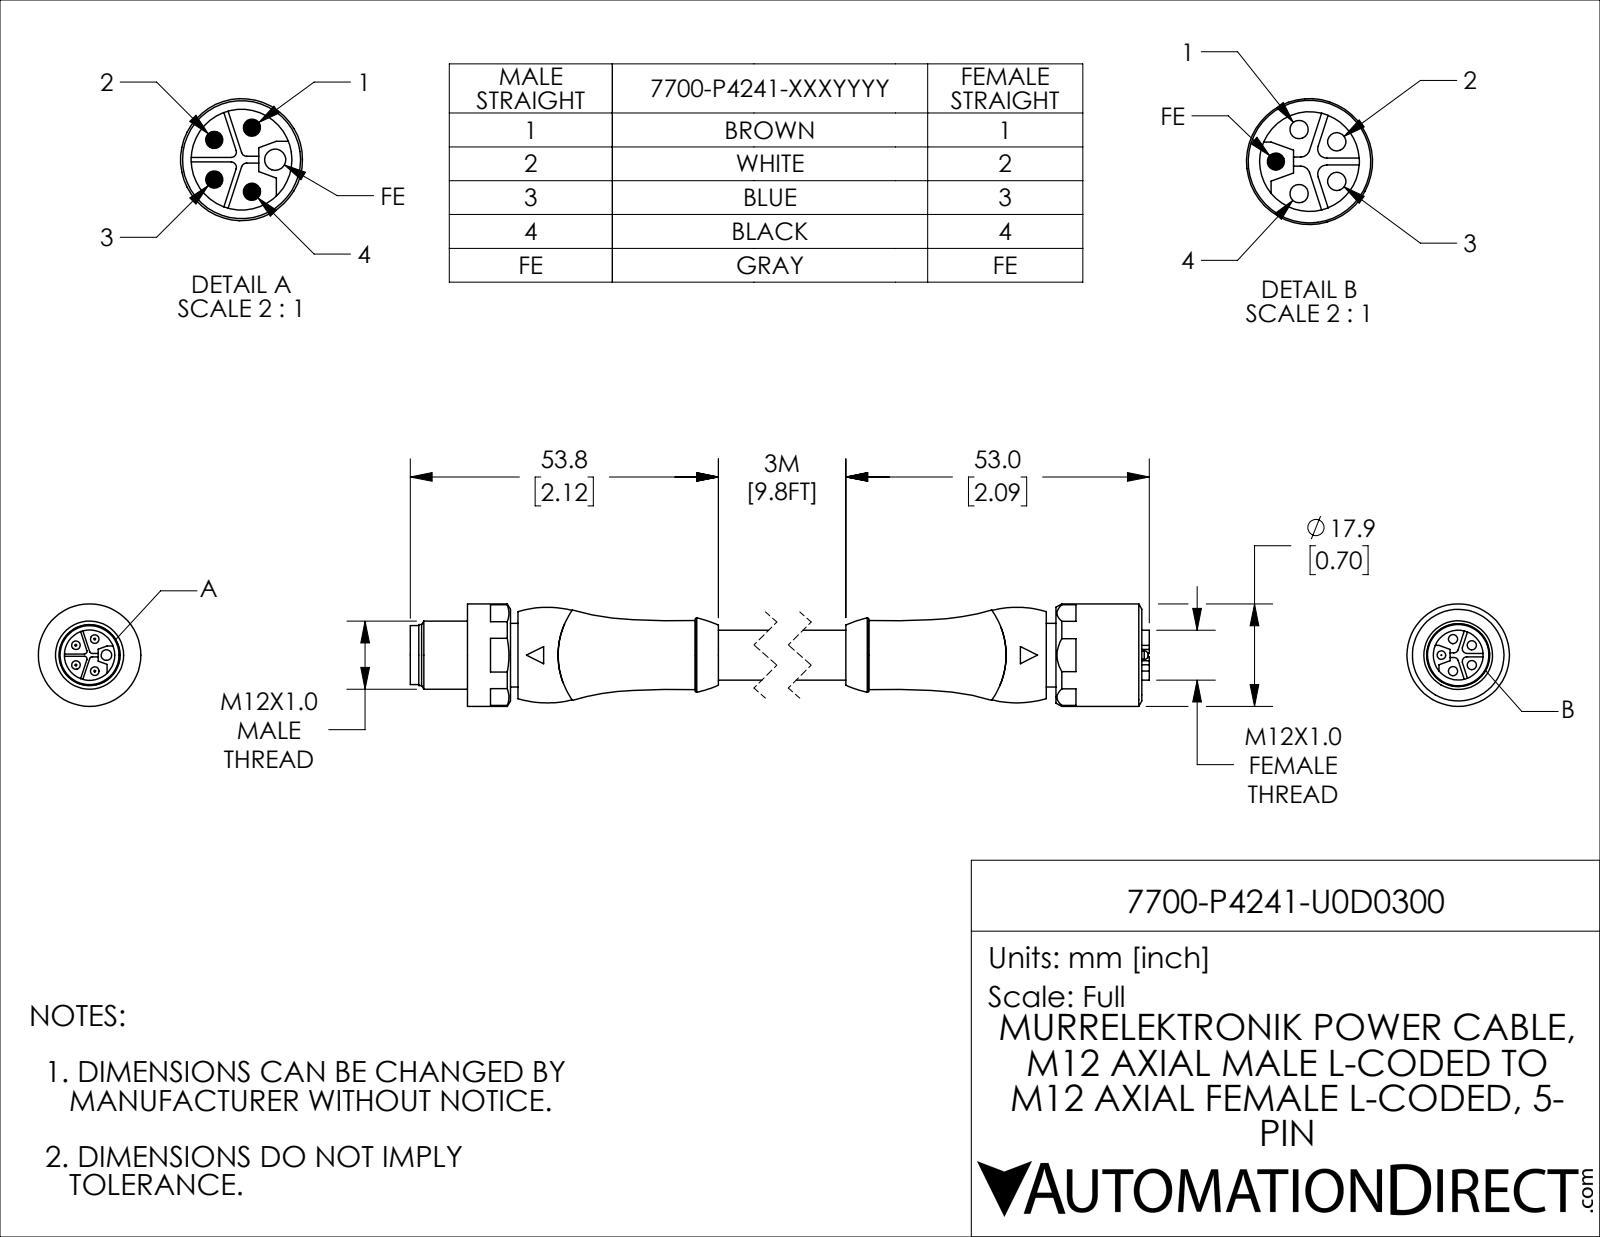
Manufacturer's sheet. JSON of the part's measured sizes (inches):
{"part_name": "7700-P4241-U0D0300_1; 7700-P4241-U0D0300_2; 7700-P4241-U0D0300", "step_written_by": "SolidWorks 2021 (CONFIG_CONTROL_DESIGN)", "units": "inches", "bodies": {"solids": 3, "faces": 214, "planar": 98, "cylindrical": 62, "other": 54}, "overall_size": [5.386, 0.705, 0.705], "volume_in3": 1.09, "surface_area_in2": 14.44, "round_holes": [[0.063, 4], [0.073, 1], [0.346, 1], [0.433, 1], [0.512, 1]], "round_bosses_or_shafts": [[0.059, 5], [0.705, 1], [0.51, 1], [0.469, 1], [0.437, 1], [0.419, 1], [0.406, 1], [0.343, 1]], "partial_cylinders_radius": [[0.018, 4], [0.031, 4]], "face_to_face_distances": [4.283, 0.067, 0.346, 0.666, 0.051, 0.295, 0.228, 4.941, 0.657, 4.35], "hole_center_spacings": [0.116, 0.136, 0.22, 0.22]}
